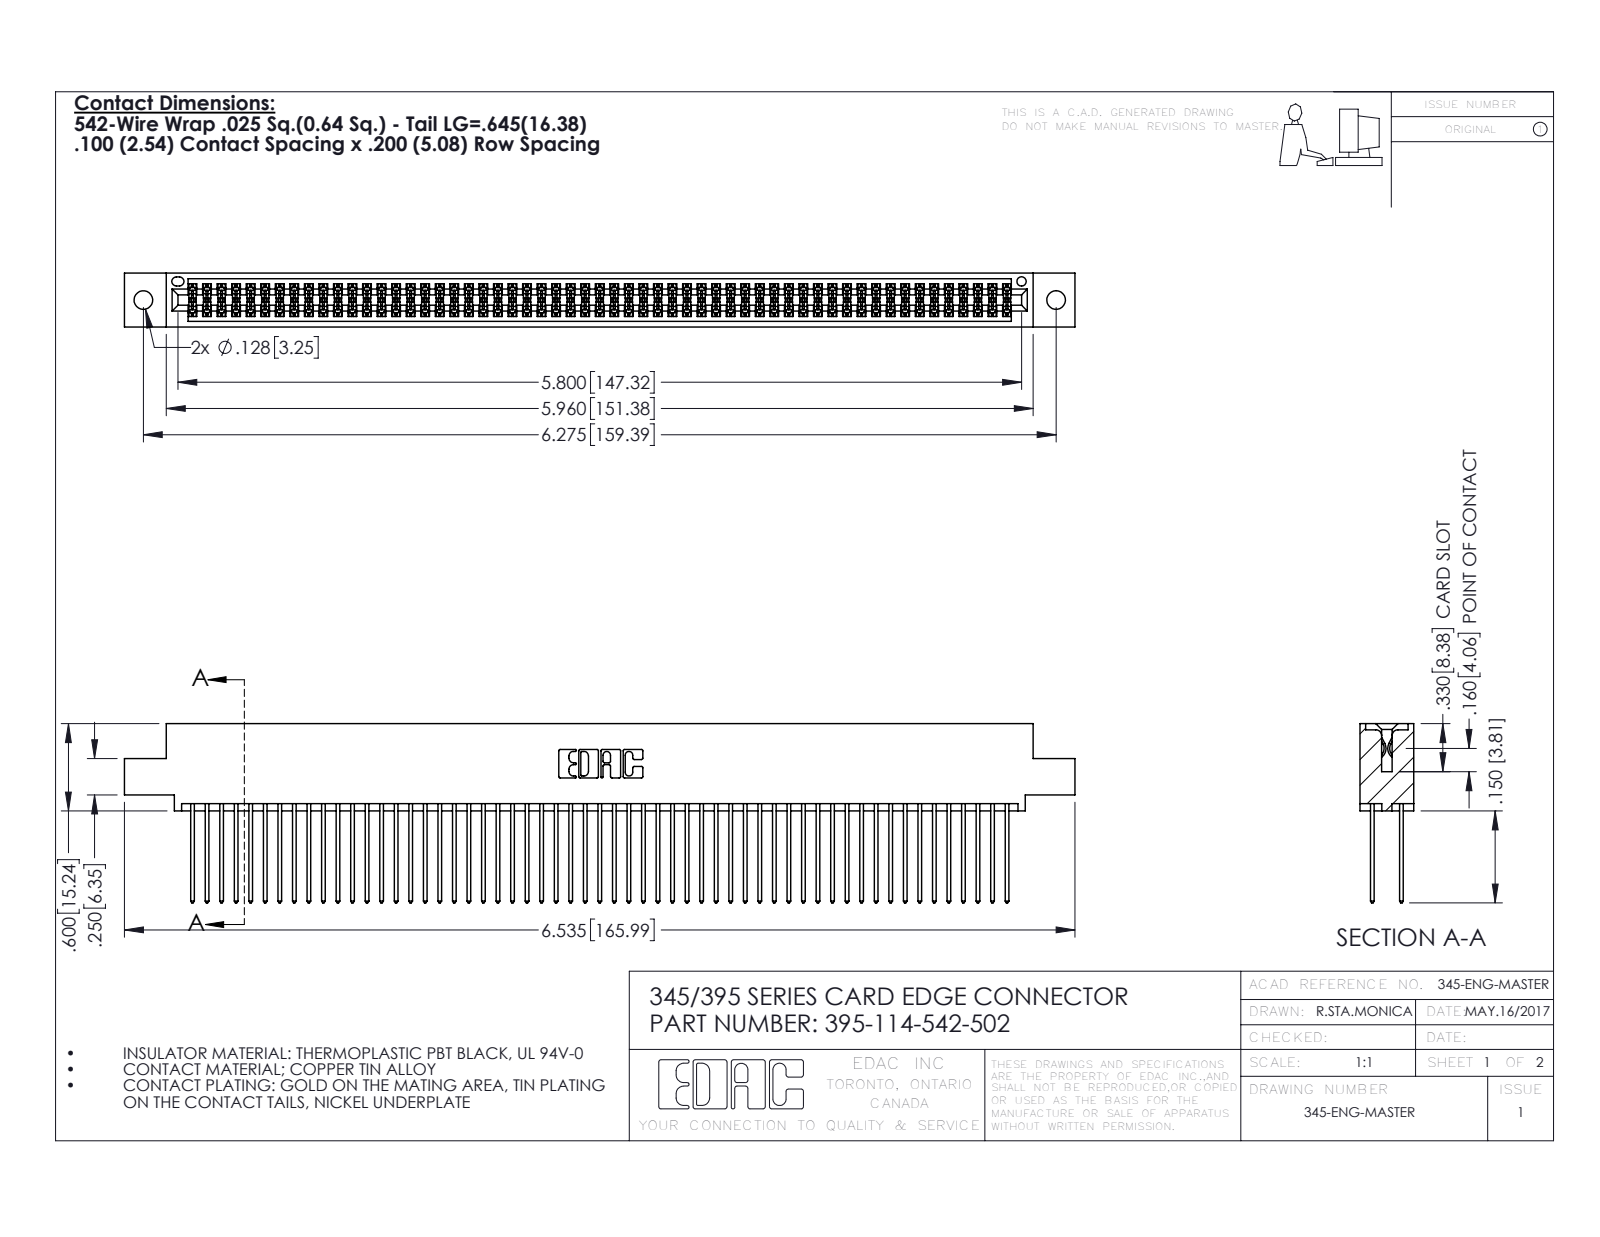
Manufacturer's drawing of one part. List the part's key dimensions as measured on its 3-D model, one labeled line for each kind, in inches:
Part name (STEP PRODUCT): 395-114-542-502; 345-292-001_345-293-142; 345 Part_0.110 Offset - 0.128 Dia
STEP written by: SolidWorks 2016 (CONFIG_CONTROL_DESIGN)
Units: inches
Bodies: 115 solids, 5830 faces (3846 planar, 1984 cylindrical, 0 other)
Overall size (bounding box): 6.535 × 1.232 × 0.37
Volume: 1.018 in³ · Surface area: 42.25 in²
Round holes (diameter × count): ⌀0.128 ×2, ⌀0.064 ×1
Partial cylindrical surfaces — rounded edges, fillets, slot ends (radius × count): R0.006 ×171, R0.01 ×114, R0.01 ×22, R0.007 ×6, R0.031 ×6, R0.026 ×3, R0.014 ×2, R0.019 ×2
Main face-to-face distances: 0.072, 0.298, 0.2, 0.098, 0.272, 0.025, 0.225, 0.37, 0.175, 0.149
Hole centre spacings: 0.27, 6.039, 6.275
